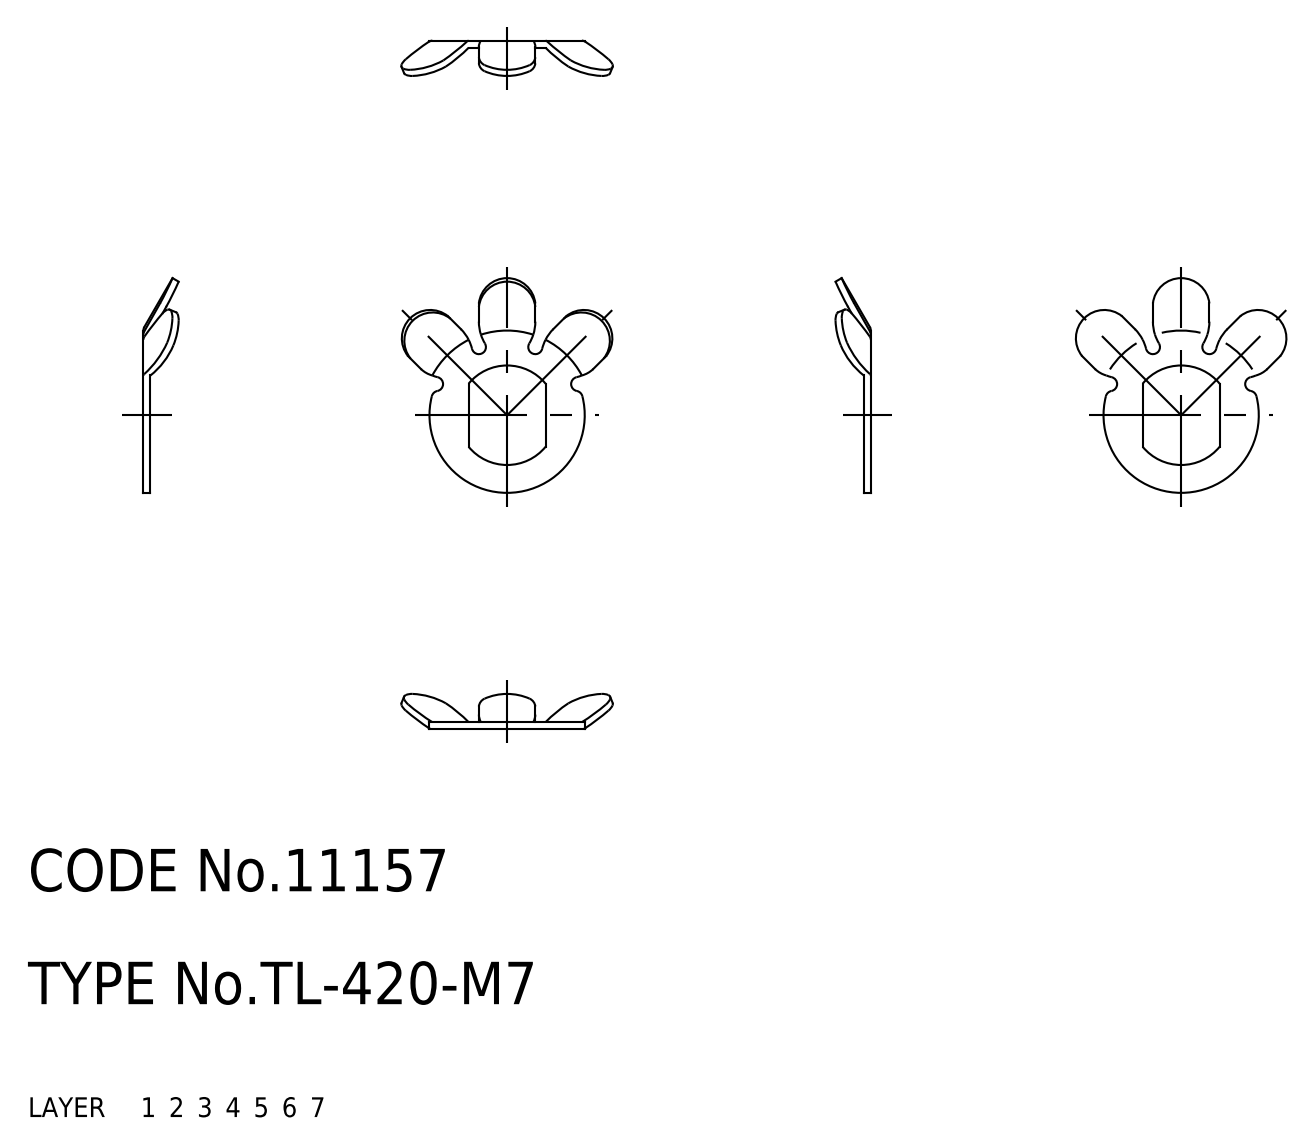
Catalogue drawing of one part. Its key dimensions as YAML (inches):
part_name: "TL_420_M7; washer"
step_written_by: "SolidWorks 2015 (AUTOMOTIVE_DESIGN)"
units: inches
bodies: {solids: 1, faces: 45, planar: 10, cylindrical: 26, other: 9}
overall_size: [0.599, 0.59, 0.098]
volume: 0.003
surface_area: 0.405
partial_cylinders:
  - {radius: 0.02, count: 6}
  - {radius: 0.118, count: 6}
  - {radius: 0.079, count: 3}
  - {radius: 0.139, count: 1}
  - {radius: 0.217, count: 1}
face_to_face_distances: [0.02, 0.215, 0.157, 0.029, 0.186]
